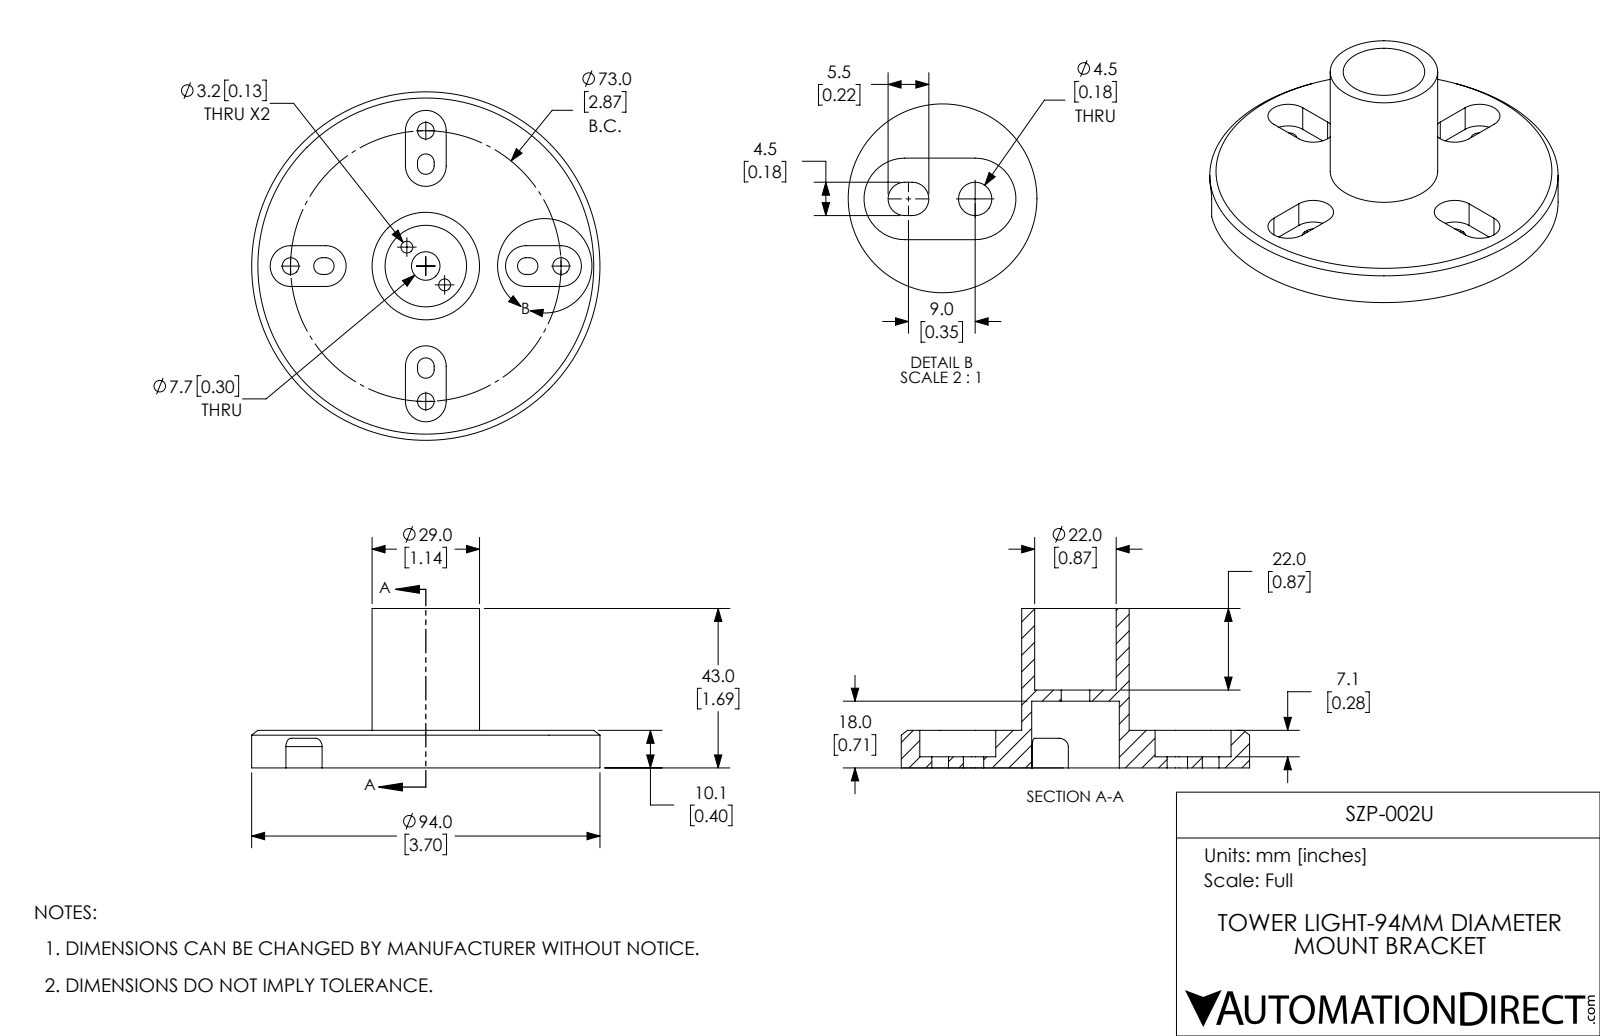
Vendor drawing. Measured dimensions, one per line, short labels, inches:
name: SZP-002U
written by: SolidWorks 2017 (AUTOMOTIVE_DESIGN)
unit: in
bodies: 1 solid, 78 faces (28 planar, 48 cylindrical, 2 other)
size: 3.701 × 3.701 × 1.693
volume: 3.985 in³; area: 37.78 in²
holes: 4× ⌀0.177, 2× ⌀0.126, 1× ⌀0.303, 1× ⌀0.866, 1× ⌀0.931
bosses: 1× ⌀3.701, 1× ⌀1.142
rounds: 10× R0.089, 8× R0.217
face distances: 0.399, 0.118, 0.709, 0.281, 0.591, 0.309, 0.315, 0.197, 0.084, 0.394
hole spacings: 1.437, 2.032, 0.283, 1.252, 1.254, 1.436, 1.438, 1.649
